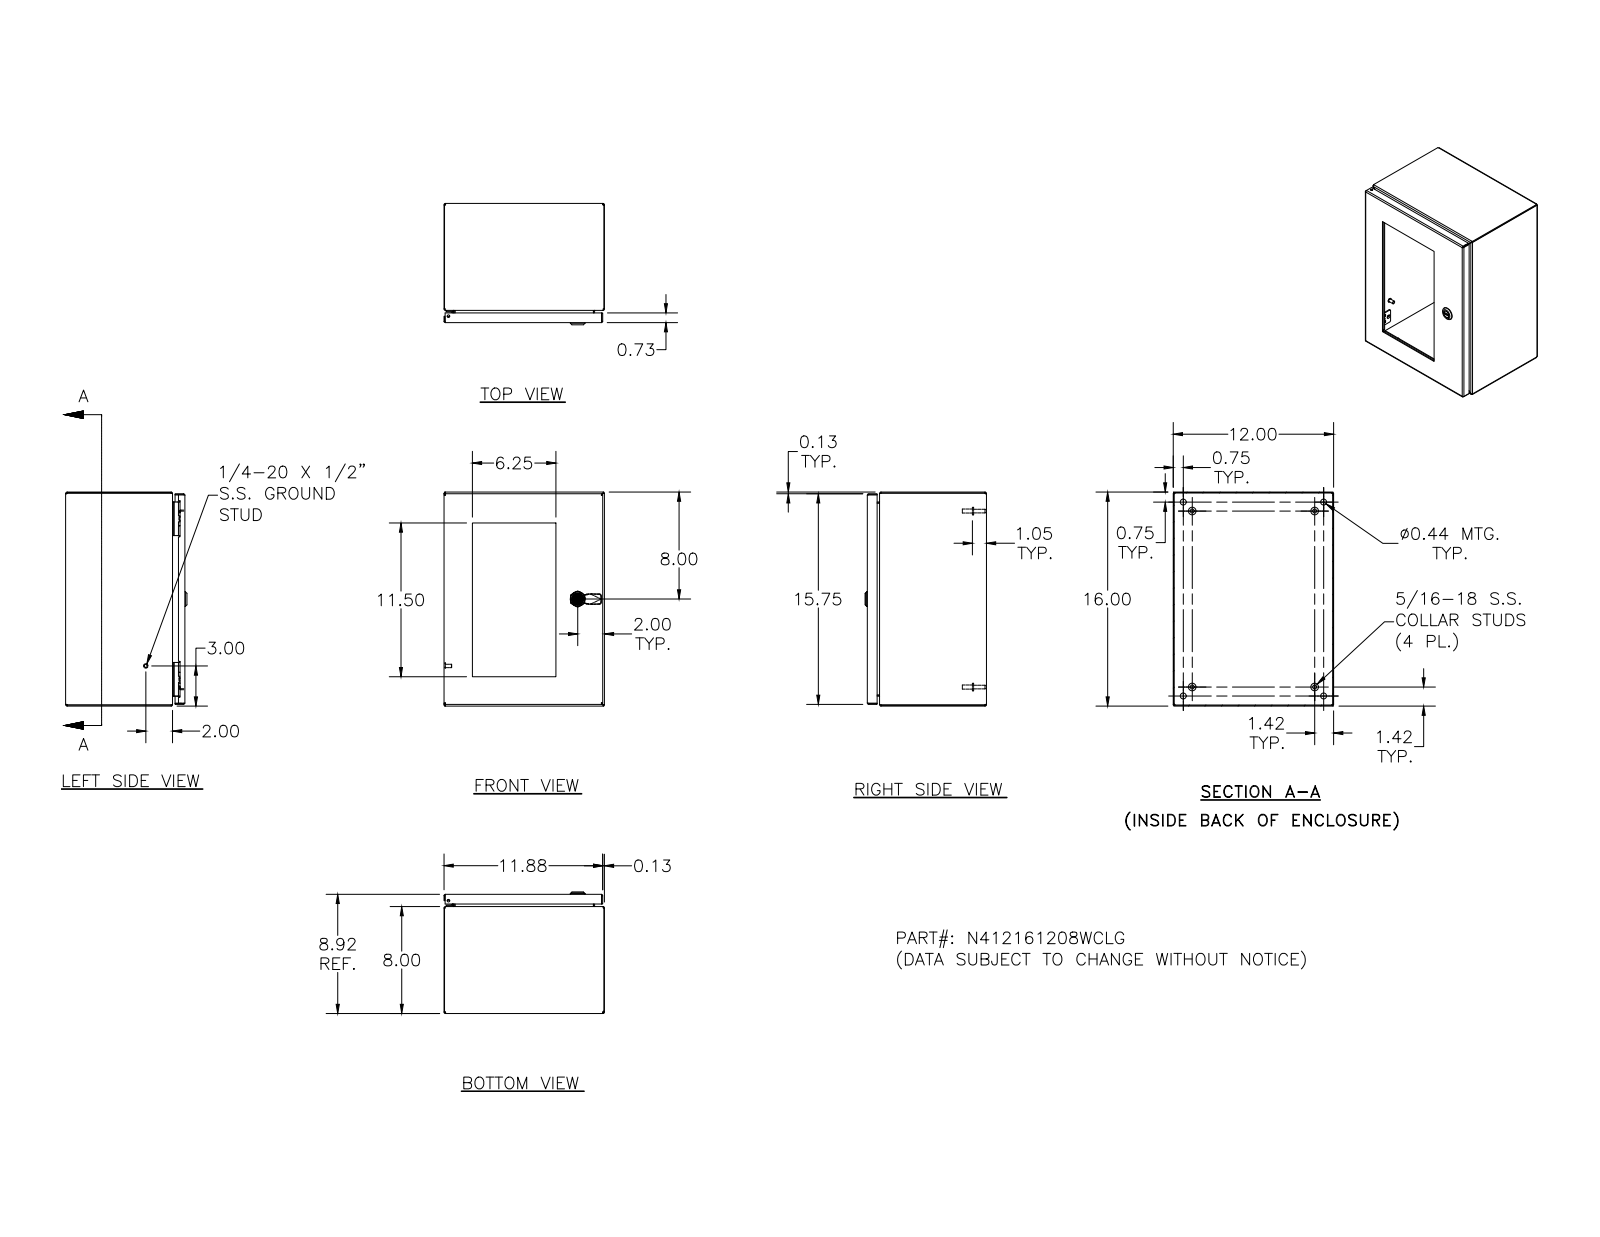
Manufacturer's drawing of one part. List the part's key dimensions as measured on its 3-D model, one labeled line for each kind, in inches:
Part name (STEP PRODUCT): N412161208WCLG
STEP written by: SolidWorks 2018 (AUTOMOTIVE_DESIGN)
Units: inches
Bodies: 57 solids, 1827 faces (687 planar, 593 cylindrical, 547 other)
Overall size (bounding box): 16 × 12 × 9.075
Volume: 91.16 in³ · Surface area: 2 069 in²
Round holes (diameter × count): ⌀0.156 ×12, ⌀0.281 ×10, ⌀0.188 ×5, ⌀0.093 ×4, ⌀0.152 ×4, ⌀0.167 ×4, ⌀0.172 ×4, ⌀0.437 ×4, ⌀0.187 ×1, ⌀0.197 ×1, ⌀0.315 ×1, ⌀0.394 ×1
Round bosses / shafts (diameter × count): ⌀0.337 ×10, ⌀0.25 ×10, ⌀0.19 ×10, ⌀0.563 ×4, ⌀0.36 ×4, ⌀0.32 ×4, ⌀0.3 ×4, ⌀0.275 ×4
Partial cylindrical surfaces — rounded edges, fillets, slot ends (radius × count): R0.031 ×34, R0.012 ×30, R0.05 ×26, R0.105 ×24, R0.016 ×18, R0.125 ×16, R0.02 ×13, R0.032 ×8
Main face-to-face distances: 0.074, 8.843, 11.926, 15.926, 8.769, 12, 11.852, 8.917, 15.852, 16
Hole centre spacings: 4, 12, 6.221, 8.5, 8.585, 11.862, 7.5, 0.5
